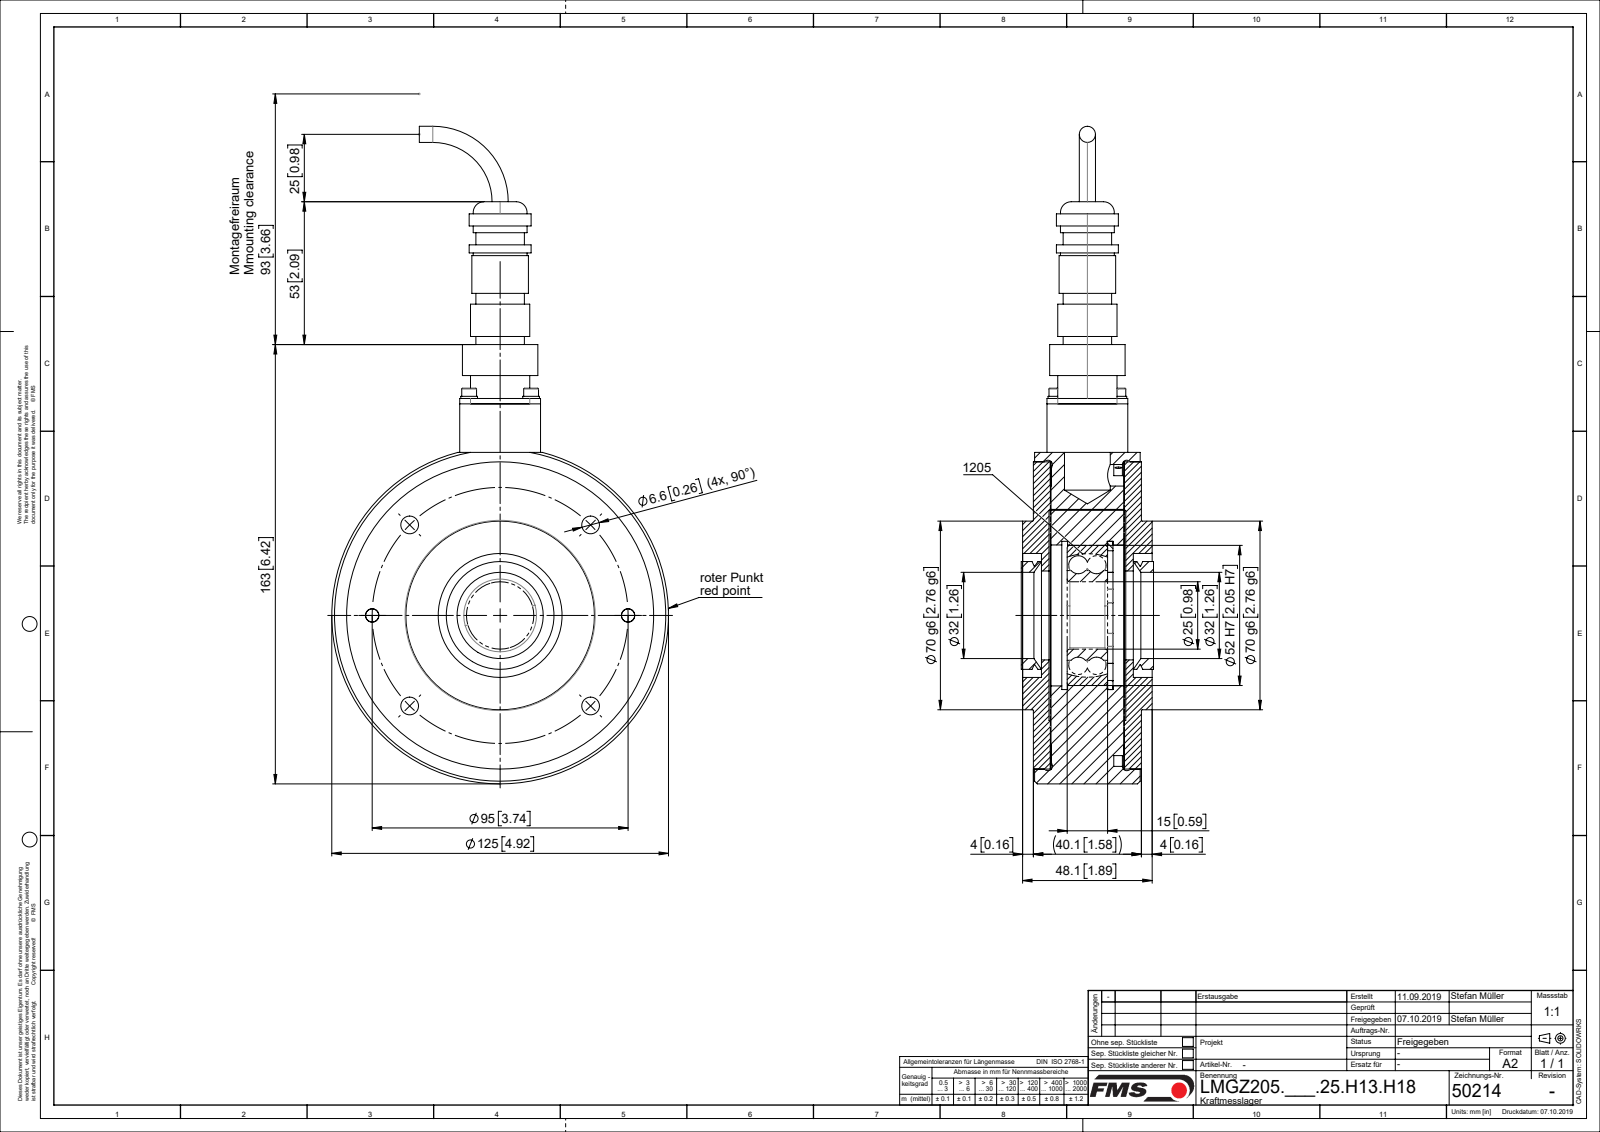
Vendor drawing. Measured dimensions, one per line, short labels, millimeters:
name: L50214; L4832404; L48964; TEIL1 (+8 more)
written by: Mechanical Desktop 2007 (CONFIG_CONTROL_DESIGN)
unit: mm
bodies: 21 solids, 413 faces (99 planar, 252 cylindrical, 62 other)
size: 244 × 125 × 48.1
volume: 490 852 mm³; area: 146 769 mm²
holes: 6× ⌀6.6, 4× ⌀2.6, 4× ⌀3.2, 4× ⌀3.4, 2× ⌀5, 2× ⌀11, 1× ⌀25, 1× ⌀31, 1× ⌀33, 1× ⌀37.9, 1× ⌀46, 1× ⌀52
bosses: 4× ⌀6.2, 4× ⌀5.5, 4× ⌀3, 4× ⌀2.5, 3× ⌀6, 2× ⌀10, 1× ⌀125, 1× ⌀114
rounds: 8× R5, 4× R4, 1× R40.5, 1× R47
face distances: 27.25, 33.55, 6.3, 6.55, 33.8, 27, 27.5, 4, 10.55, 40.1
hole spacings: 47.5, 23, 36.36, 67.18, 87.77, 32.53, 95.01, 95
